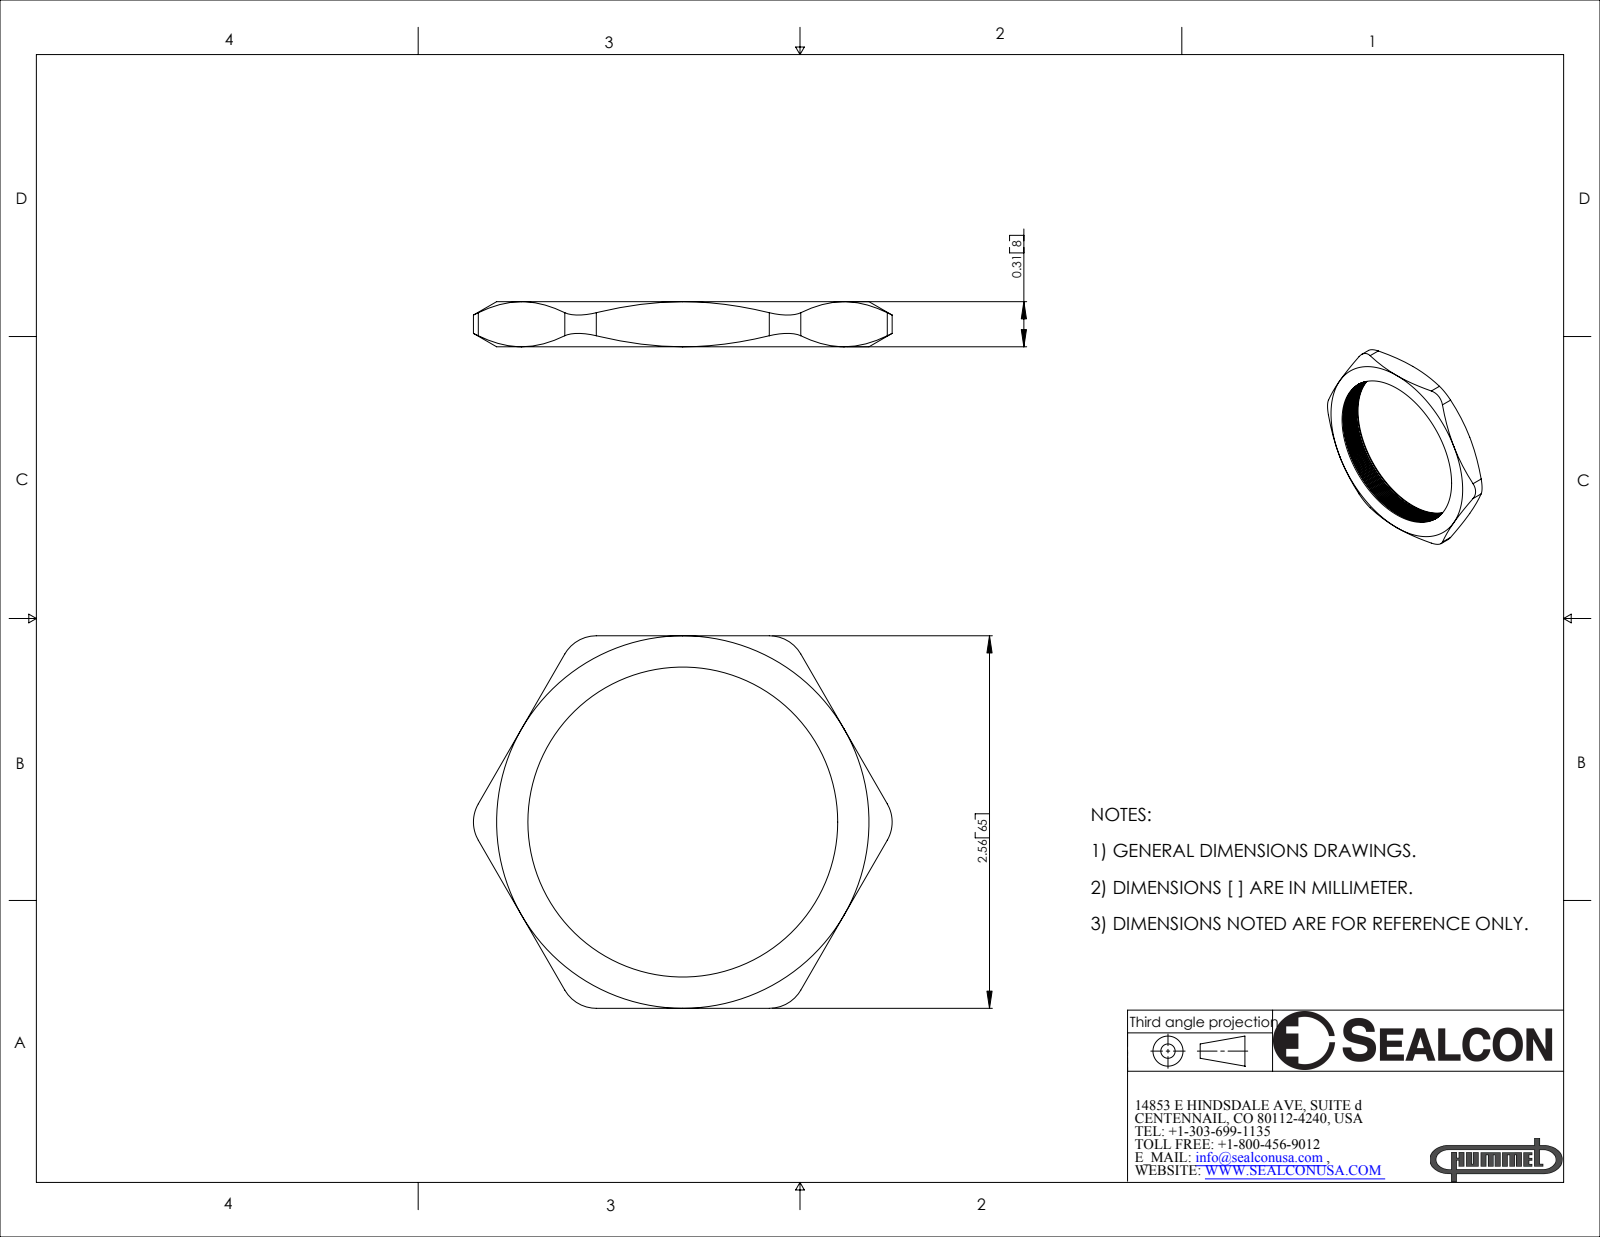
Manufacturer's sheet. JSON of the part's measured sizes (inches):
{"part_name": "NP-42", "step_written_by": "SolidWorks 2007 (CONFIG_CONTROL_DESIGN)", "units": "inches", "bodies": {"solids": 1, "faces": 101, "planar": 8, "cylindrical": 31, "other": 62}, "overall_size": [2.879, 2.56, 0.31], "volume_in3": 0.597, "surface_area_in2": 10.36, "round_holes": [[2.13, 1]], "partial_cylinders_radius": [[0.25, 6]], "face_to_face_distances": [0.31, 2.56]}
